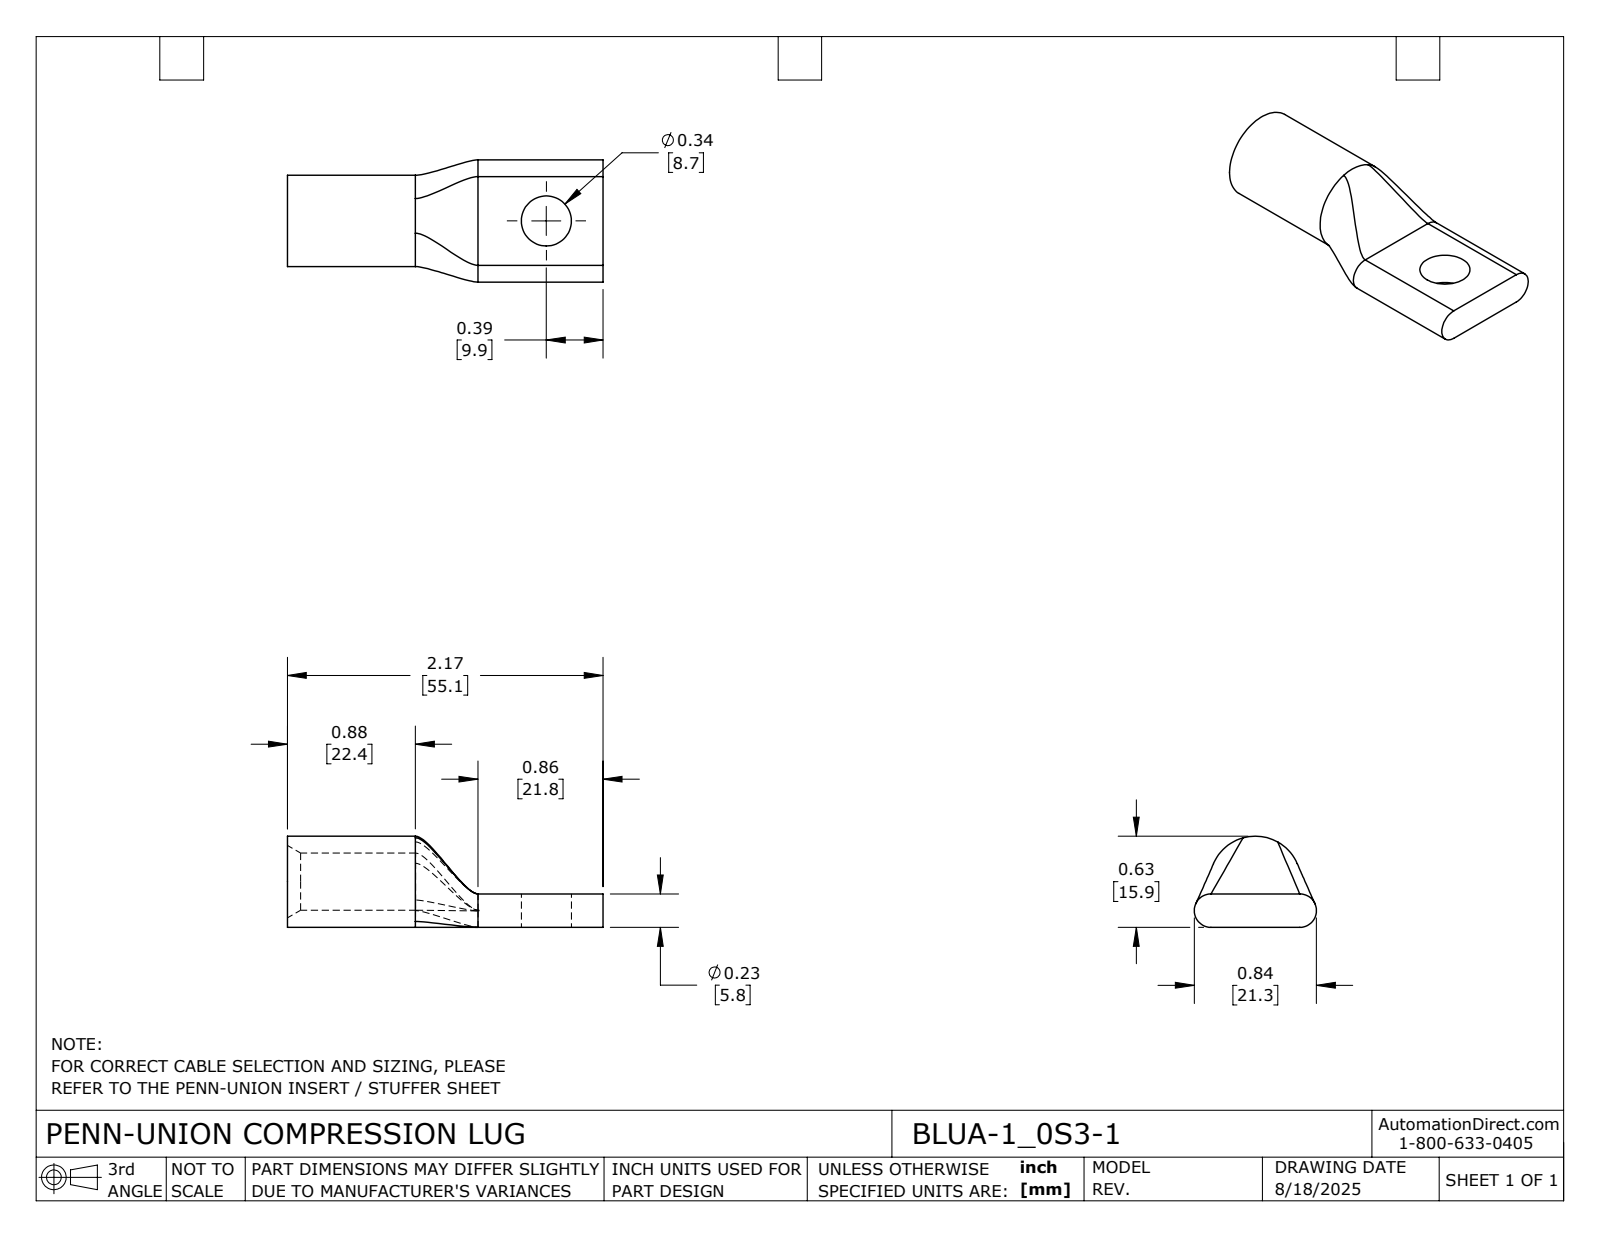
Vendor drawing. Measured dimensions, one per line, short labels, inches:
name: BLUA-1_0S3-1
written by: SolidWorks 2024 (CONFIG_CONTROL_DESIGN)
unit: in
bodies: 1 solid, 24 faces (5 planar, 9 cylindrical, 10 other)
size: 2.17 × 0.84 × 0.627
volume: 0.375 in³; area: 6.406 in²
holes: 1× ⌀0.344, 1× ⌀0.393
bosses: 1× ⌀0.627
rounds: 2× R0.115
face distances: 0.23, 2.17, 1.31, 0.86
